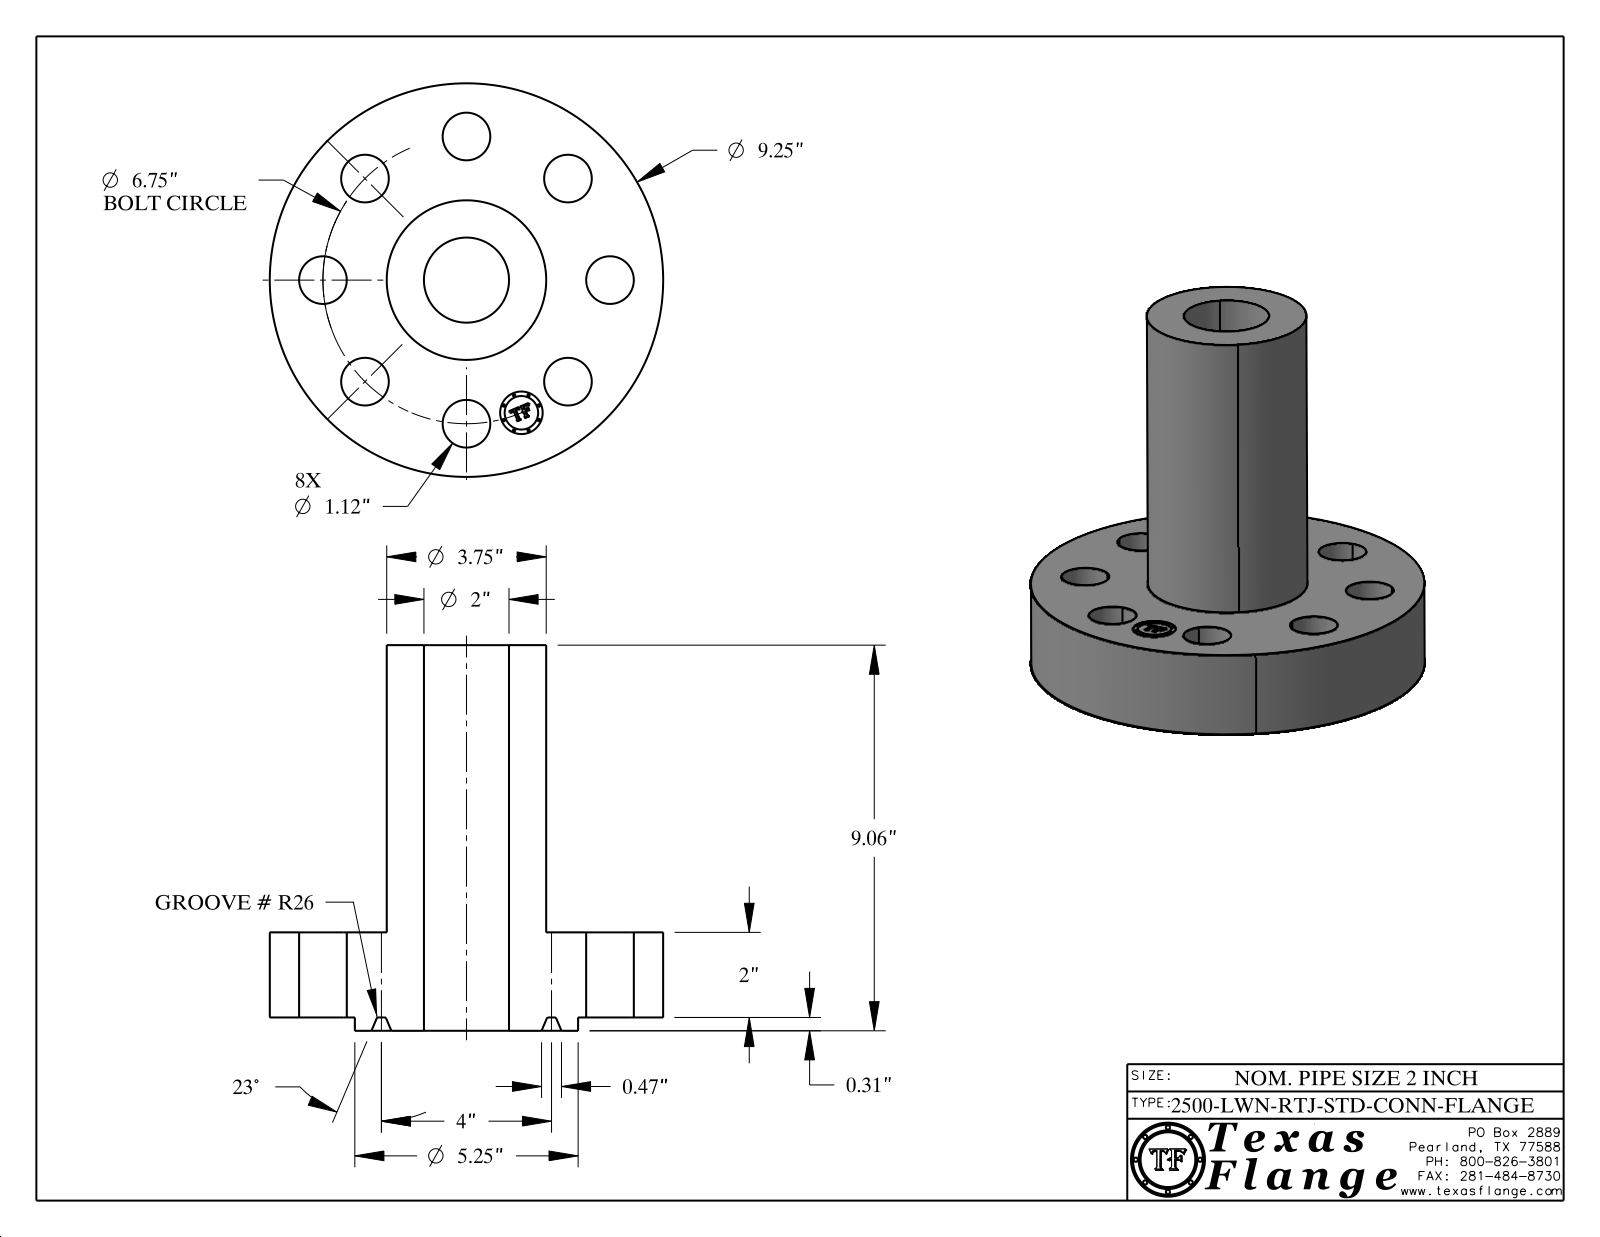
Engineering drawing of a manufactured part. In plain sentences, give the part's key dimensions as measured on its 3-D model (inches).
The part is named "2-2500-LWN-RTJ-STD-CONN-FLANGE". Its 3-D file was written by "CATIA V5 STEP AP214 (AUTOMOTIVE_DESIGN)". It is 1 solid with 423 faces: 371 planar, 44 cylindrical and 8 other. Overall it measures 9.25 by 9.25 by 9.063 inches. Its volume is 170.2 cubic inches and its surface area 373.5 square inches. Round holes: 8 of diameter 1.12, 1 of diameter 1, 1 of diameter 2. Round bosses or shafts: 8 of diameter 0.061, 1 of diameter 9.25, 1 of diameter 5.25, 1 of diameter 3.75, 1 of diameter 0.788. The main face-to-face distances are 2, 0.313, 2.313, 9.063, 8.75, 6.75, 2.308, 1.995, 6.755, 0.298. The hole center spacings are 3.375, 2.583, 4.773, 6.237, 6.75, 1.317, 5.613, 6.62.
